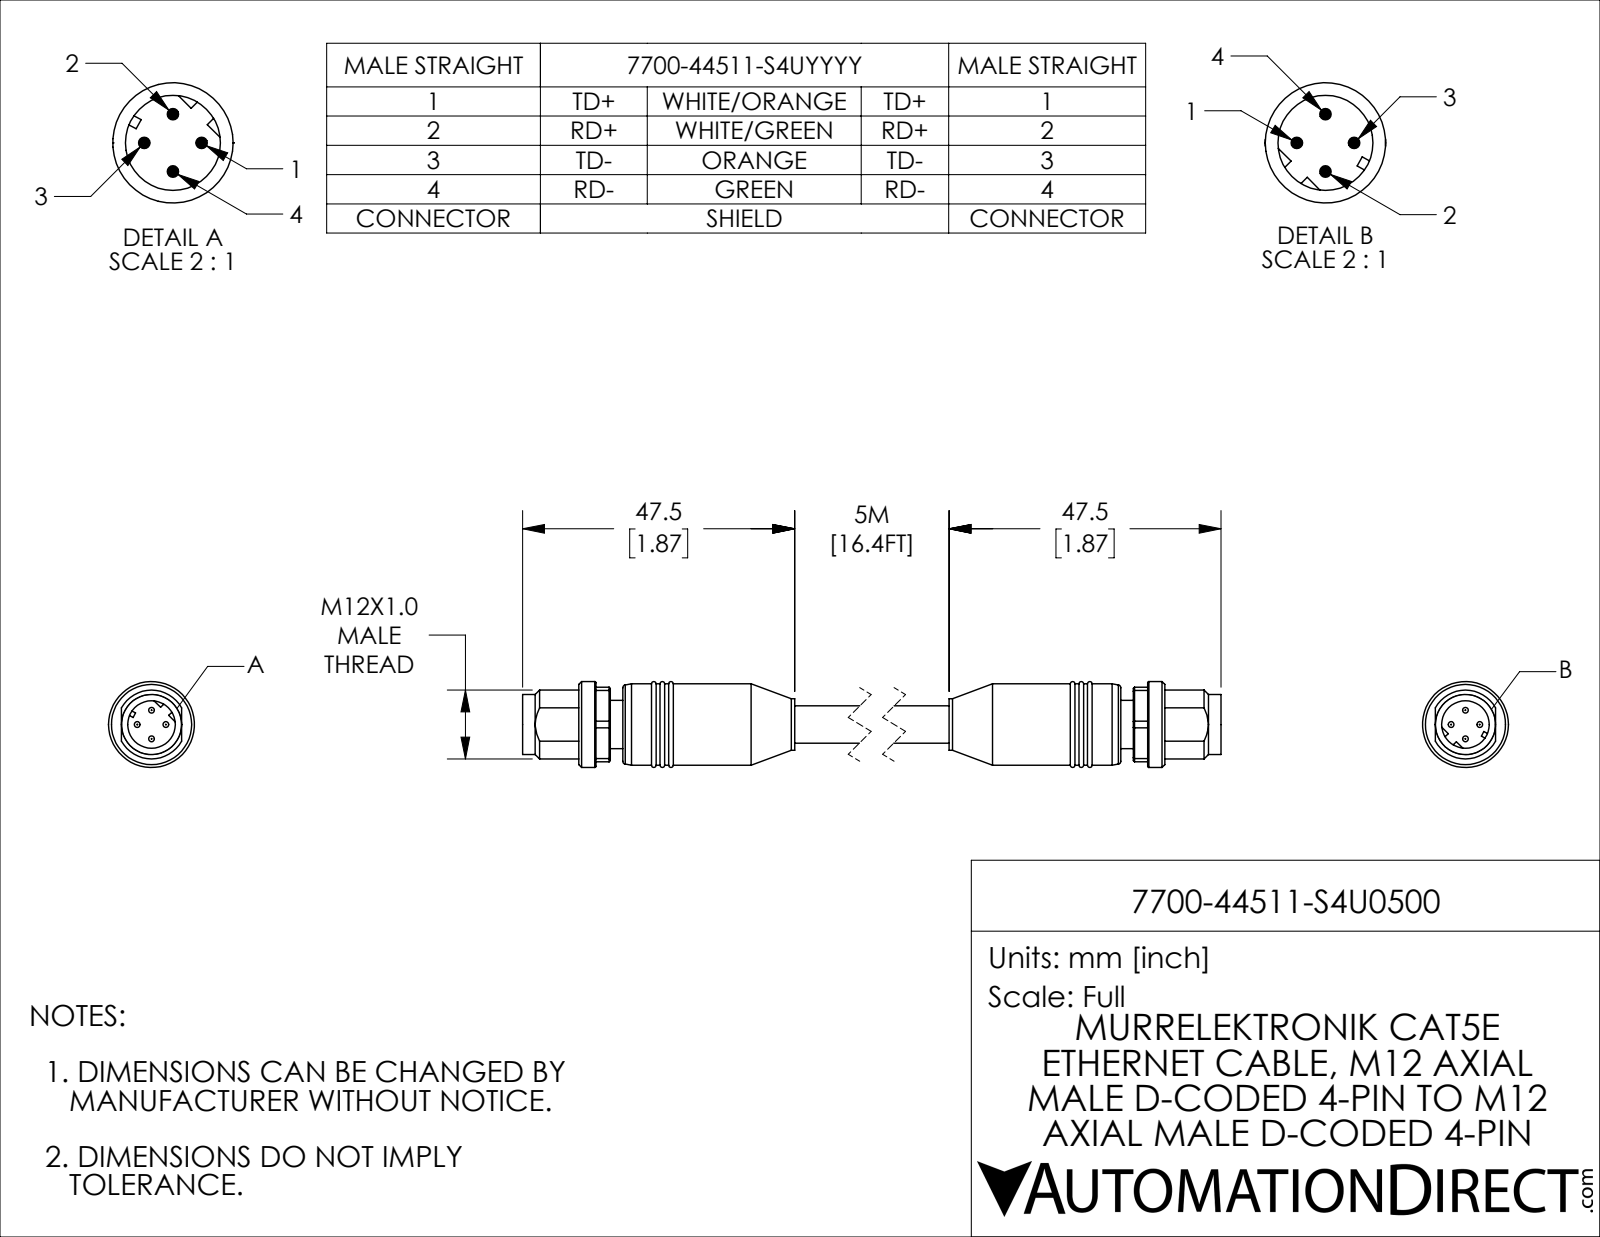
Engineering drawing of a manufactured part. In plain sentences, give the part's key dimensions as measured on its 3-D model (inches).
The part is named "7700-44511-S4U0500; 7700-44511-S4U0500_1". Its 3-D file was written by "SolidWorks 2021 (CONFIG_CONTROL_DESIGN)". It is 2 solids with 226 faces: 72 planar, 74 cylindrical and 80 other. Overall it measures 5.815 by 0.591 by 0.591 inches. Its volume is 0.804 cubic inches and its surface area 9.846 square inches. Round holes: 1 of diameter 0.327. Round bosses or shafts: 4 of diameter 0.039, 1 of diameter 0.591, 1 of diameter 0.559, 1 of diameter 0.413, 1 of diameter 0.354, 1 of diameter 0.331, 1 of diameter 0.256. Partial cylindrical surfaces (rounded edges, fillets, slot ends): 1 of radius 0.236, 1 of radius 0.283. The main face-to-face distances are 0.087, 4.524, 0.035, 0.252, 0.339, 4.776, 4.862, 5.079, 0.217, 0.303.
